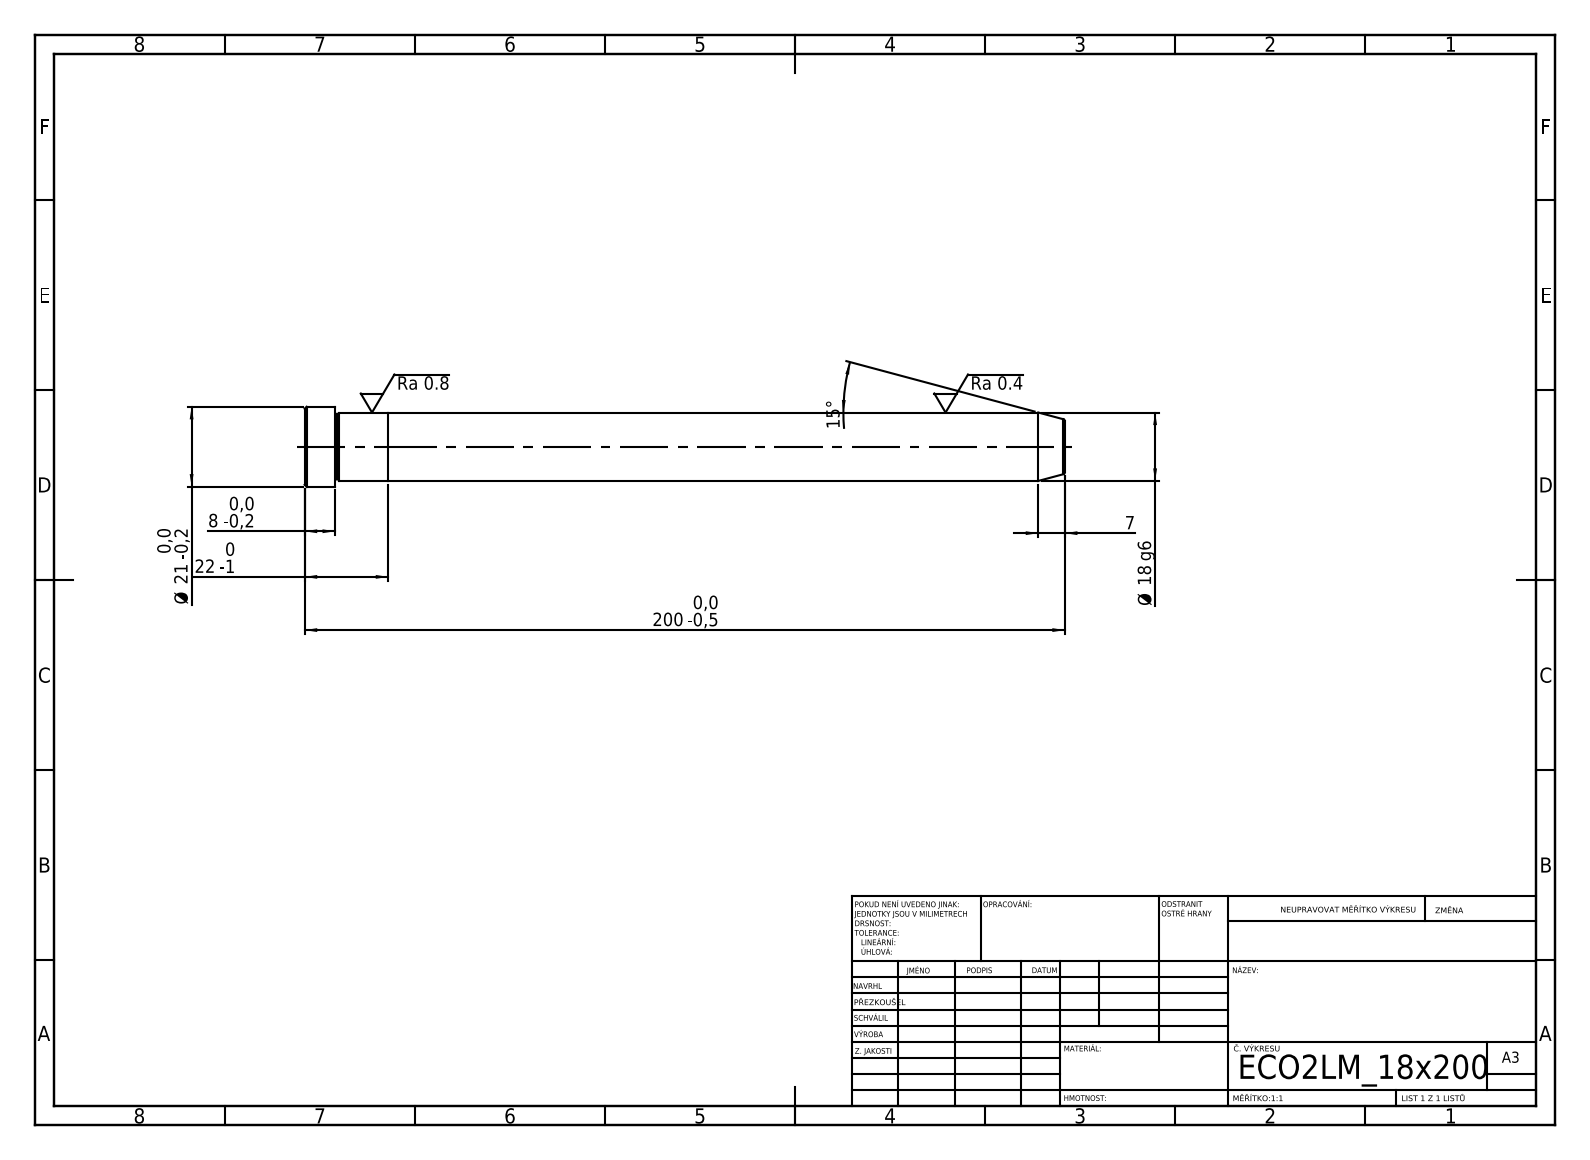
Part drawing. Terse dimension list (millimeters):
written by: SolidWorks 2019 (CONFIG_CONTROL_DESIGN)
unit: mm
bodies: 2 solids, 21 faces (5 planar, 6 cylindrical, 10 other)
size: 200 × 21 × 21
volume: 51 252 mm³; area: 12 467 mm²
bosses: 1× ⌀21, 1× ⌀18
face distances: 22, 178, 200, 192, 14, 8
